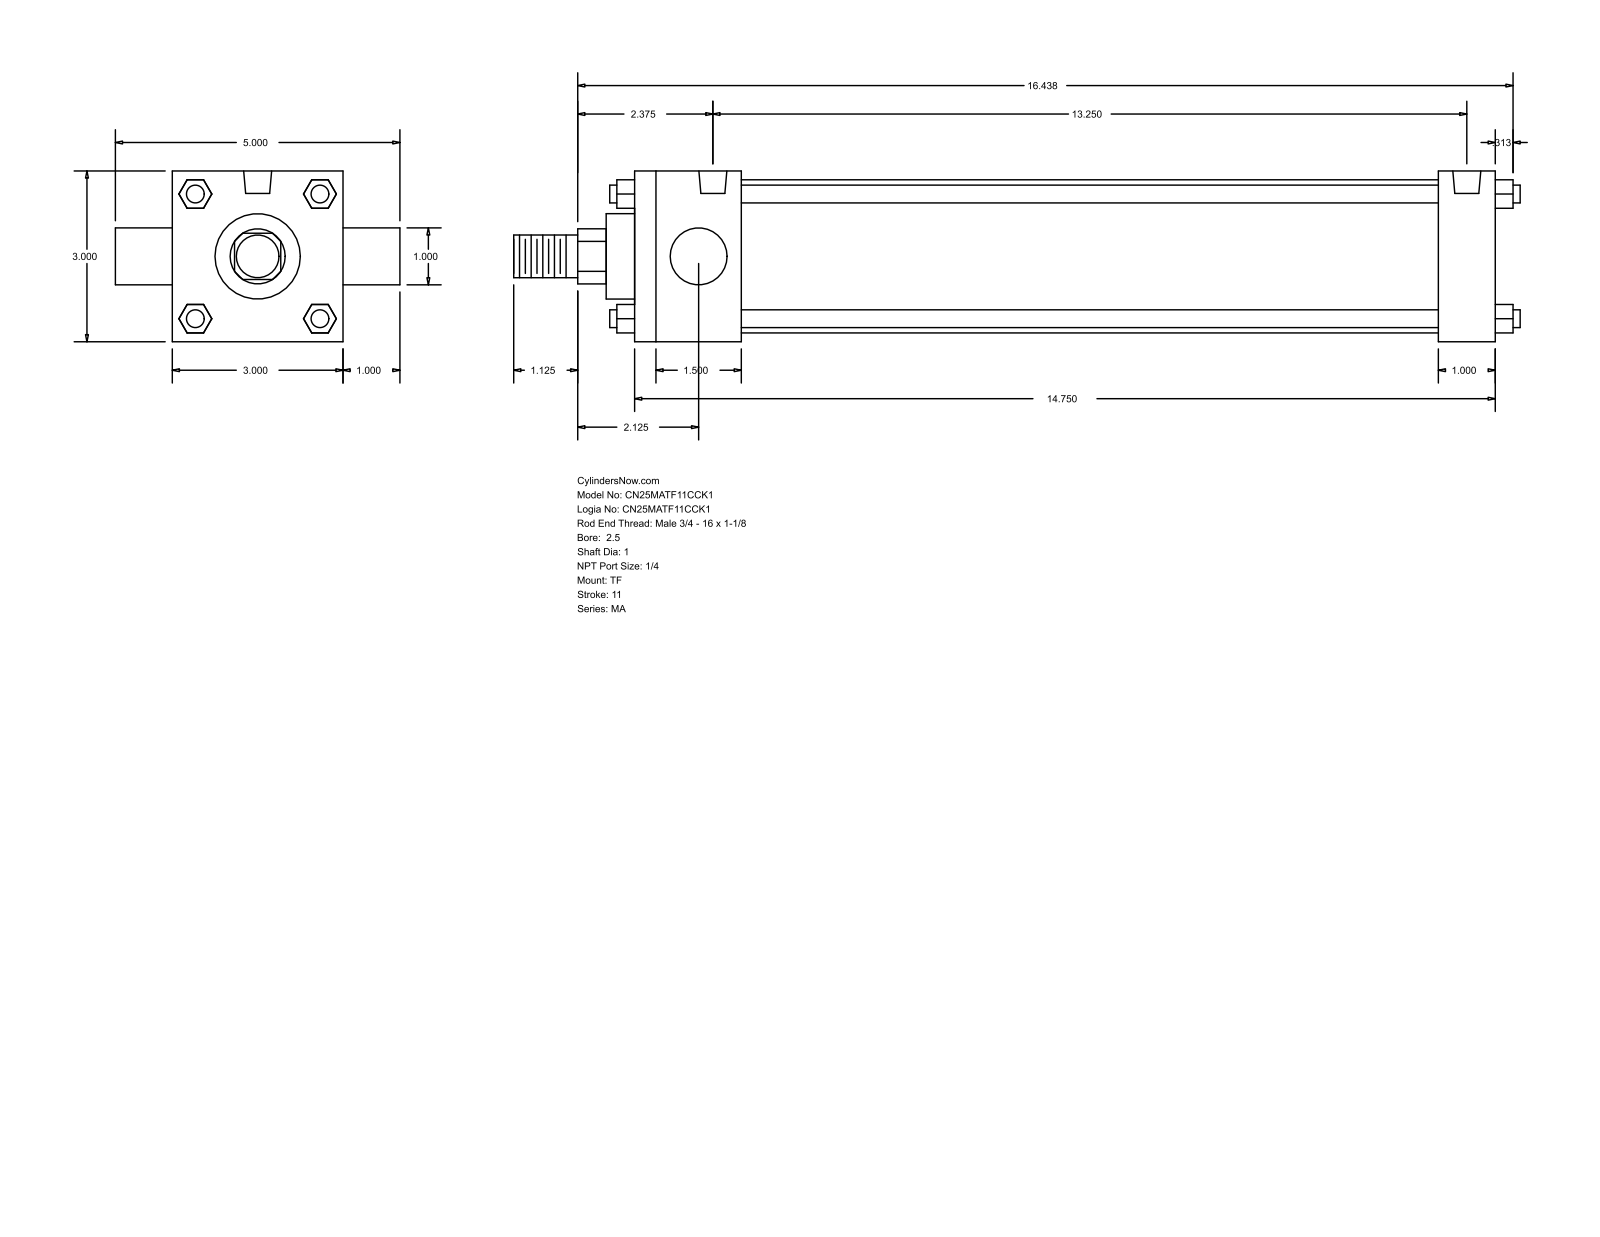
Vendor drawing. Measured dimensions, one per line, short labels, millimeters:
name: MA_TF__0250_1
written by: GSSL Pune (CONFIG_CONTROL_DESIGN)
unit: mm
bodies: 0 solids, 120 faces (92 planar, 28 cylindrical, 0 other)
size: 449.26 × 127 × 76.2
holes: 3× ⌀7.94, 2× ⌀12.49
bosses: 4× ⌀7.94, 2× ⌀25.4, 1× ⌀68.33, 1× ⌀38.1, 1× ⌀19.05
rounds: 1× R12.29
face distances: 76.2, 384.17, 12.7, 47.63, 358.78, 311.15, 336.54, 25.39, 101.6, 25.4
hole spacings: 336.55
